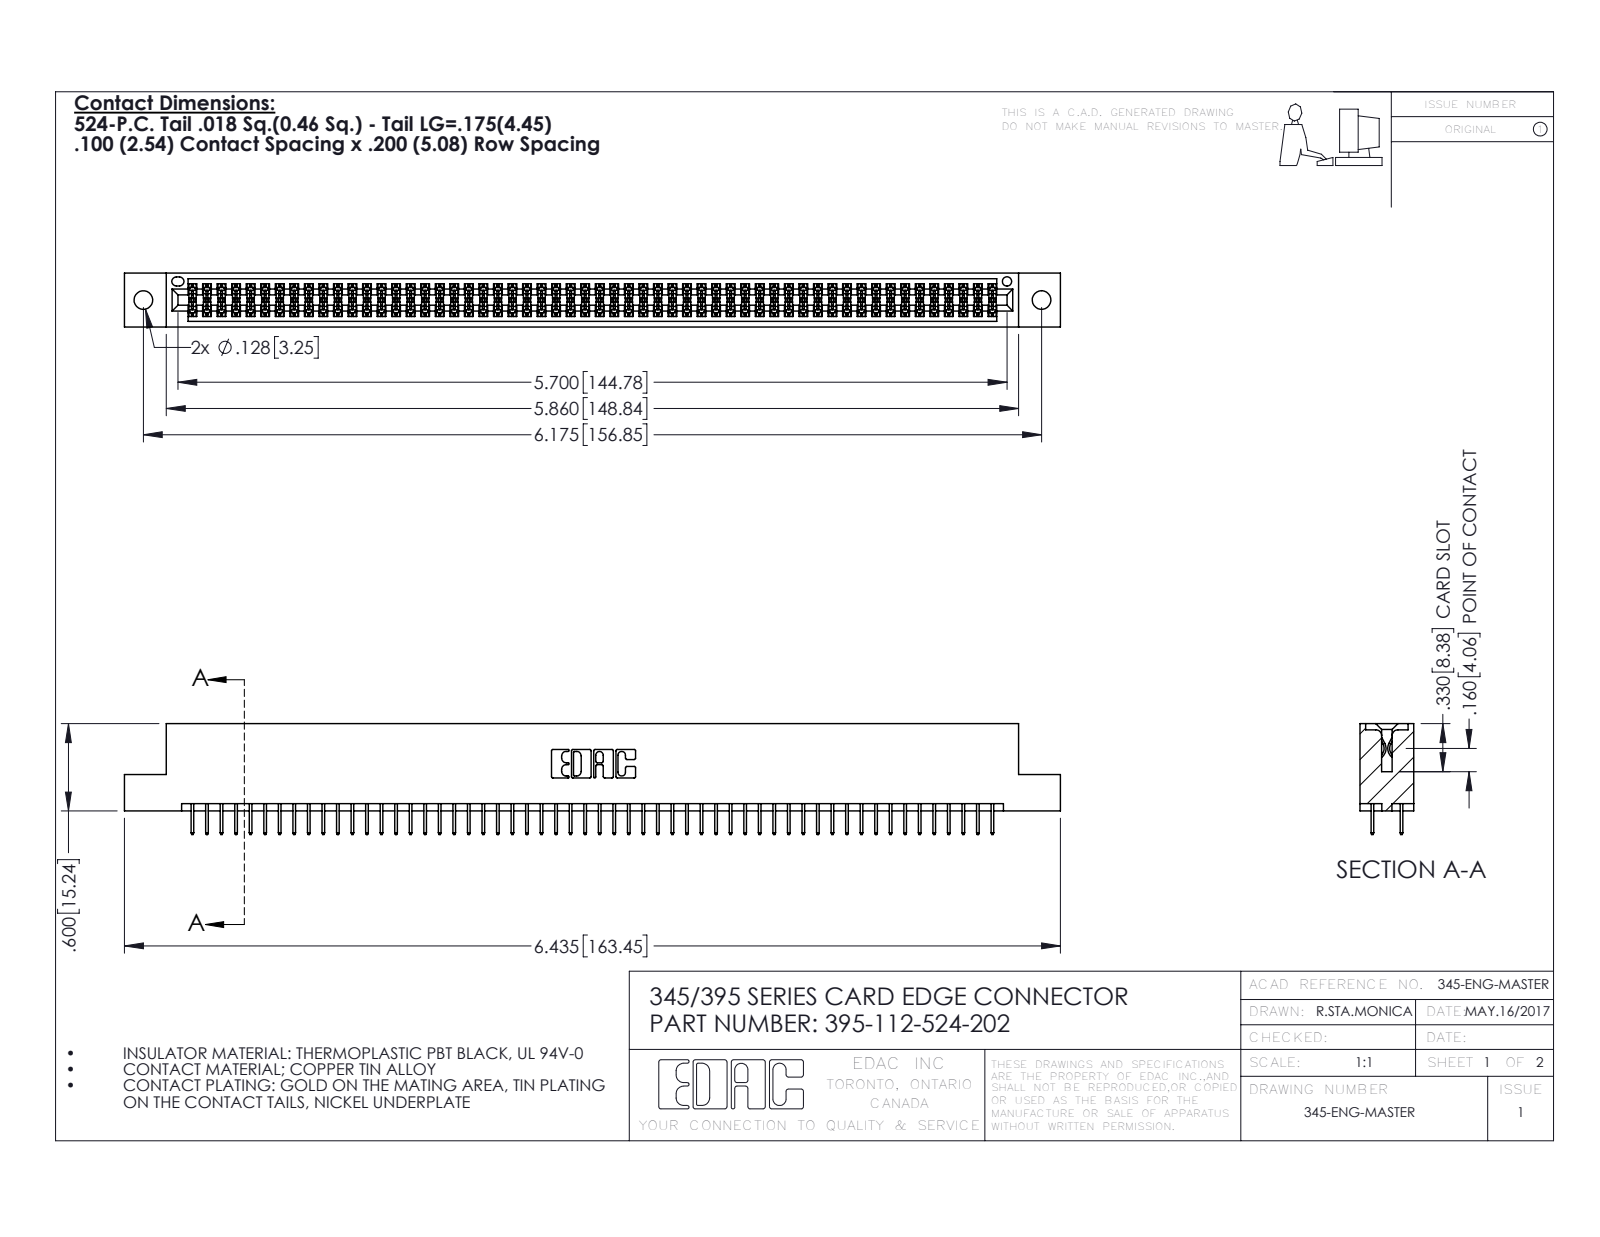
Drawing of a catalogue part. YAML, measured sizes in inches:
part_name: "345 Part_Flush Mounting Lugs - 0.128 Dia; 395-112-524-202; 345-292-001_345-293-124"
step_written_by: "SolidWorks 2016 (CONFIG_CONTROL_DESIGN)"
units: inches
bodies: {solids: 113, faces: 6174, planar: 4448, cylindrical: 1726, other: 0}
overall_size: [6.435, 0.762, 0.37]
volume: 0.964
surface_area: 35.51
round_holes:
  - {diameter: 0.128, count: 2}
  - {diameter: 0.064, count: 1}
partial_cylinders:
  - {radius: 0.006, count: 168}
  - {radius: 0.01, count: 22}
  - {radius: 0.007, count: 6}
  - {radius: 0.031, count: 6}
  - {radius: 0.026, count: 3}
  - {radius: 0.014, count: 2}
  - {radius: 0.019, count: 2}
  - {radius: 0.022, count: 2}
face_to_face_distances: [0.072, 0.298, 0.2, 0.37, 0.098, 0.272, 0.025, 0.225, 0.072, 0.175]
hole_center_spacings: [0.27, 5.939, 6.175]
